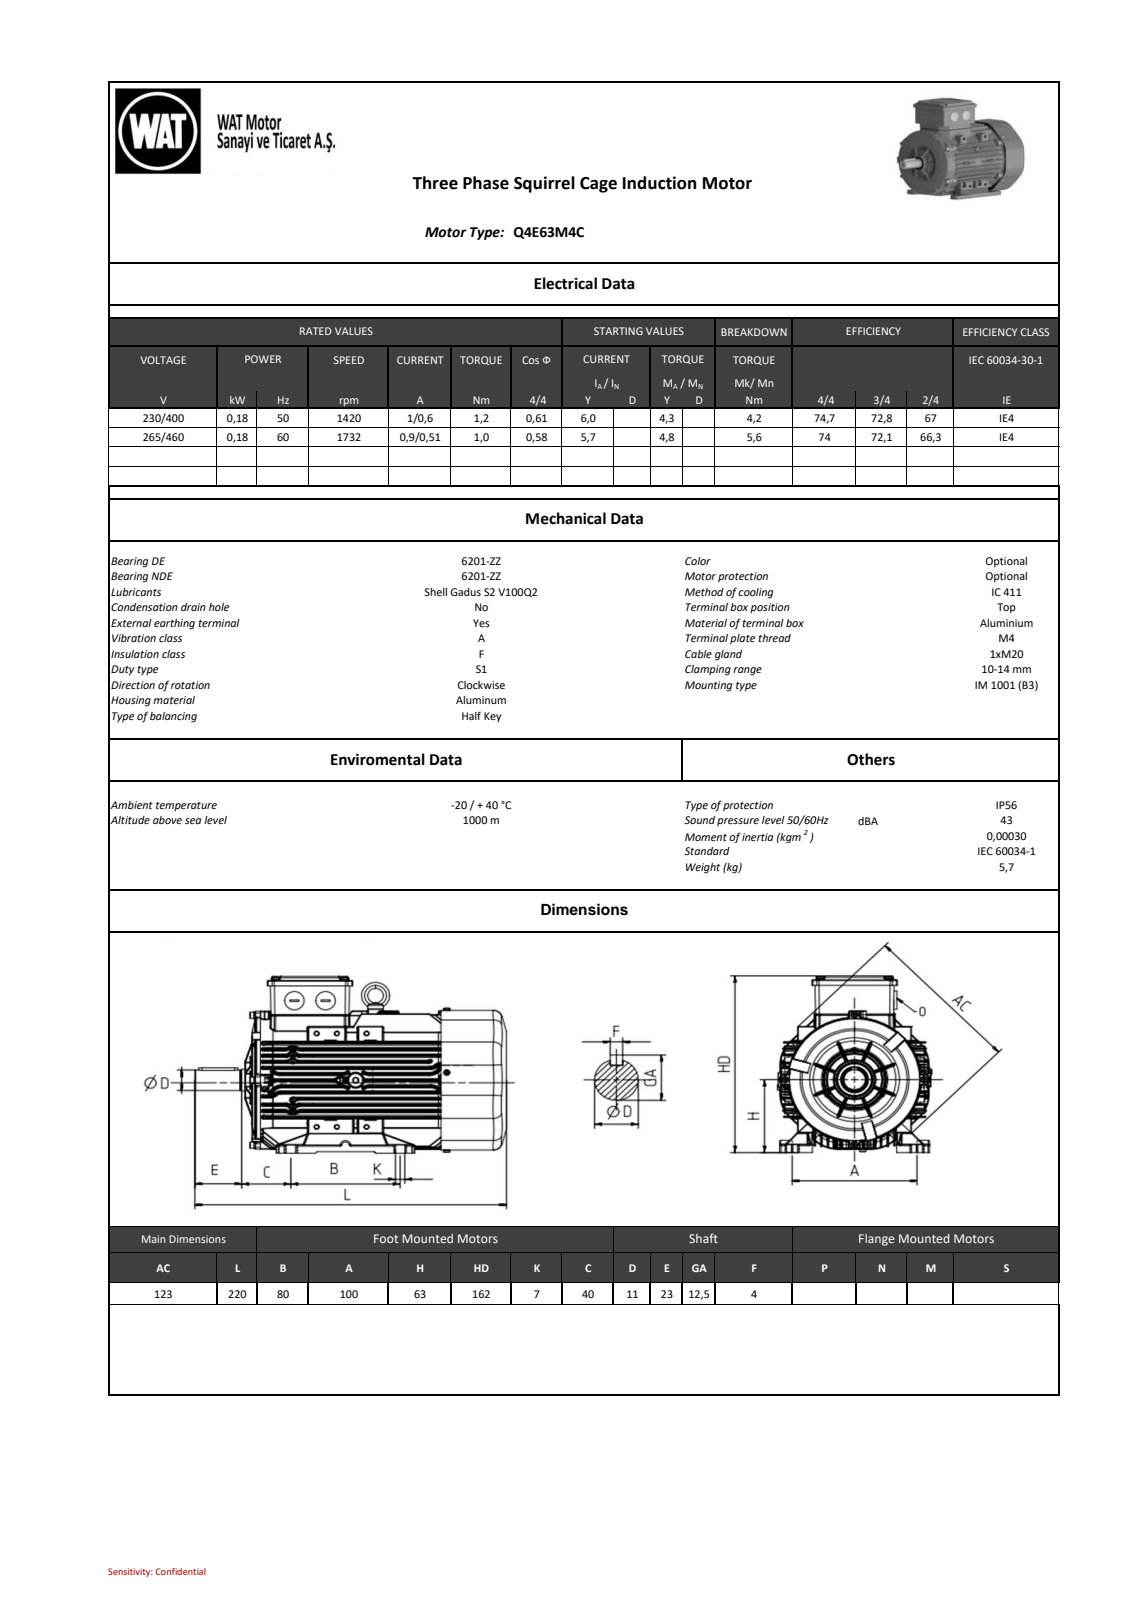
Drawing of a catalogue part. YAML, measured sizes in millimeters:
part_name: "QS63ASB3_GMM"
step_written_by: "UNIX (AUTOMOTIVE_DESIGN)"
units: millimeters
bodies: {solids: 4, faces: 2864, planar: 0, cylindrical: 0, other: 2864}
overall_size: [220.76, 161.1, 128]
